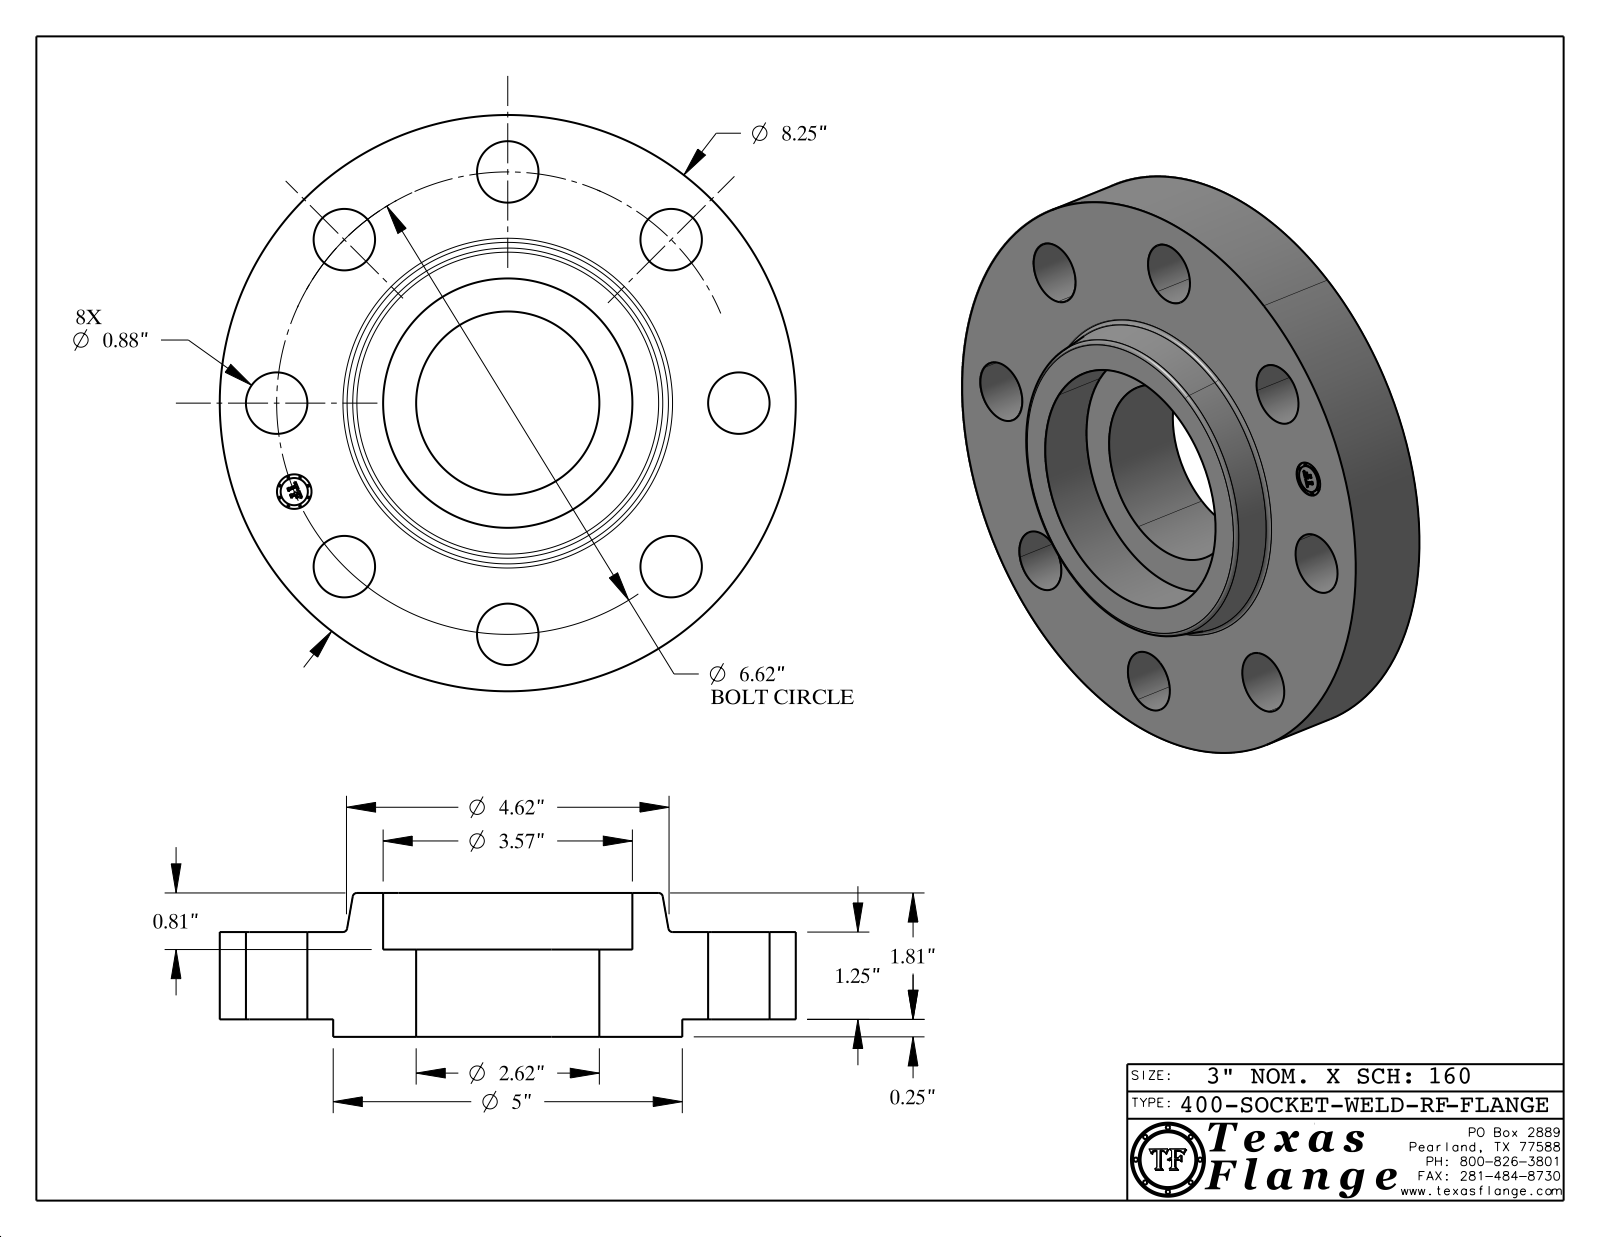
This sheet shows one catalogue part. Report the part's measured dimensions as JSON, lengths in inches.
{"part_name": "400-SOCKET-WELD-RF", "step_written_by": "CATIA V5 STEP AP214 (AUTOMOTIVE_DESIGN)", "units": "inches", "bodies": {"solids": 1, "faces": 420, "planar": 370, "cylindrical": 44, "other": 6}, "overall_size": [8.25, 8.25, 2.06], "volume_in3": 59.77, "surface_area_in2": 176, "round_holes": [[0.88, 8], [0.495, 1], [2.624, 1], [3.57, 1]], "round_bosses_or_shafts": [[0.03, 8], [8.25, 1], [5, 1], [0.39, 1]], "face_to_face_distances": [1.25, 0.25, 1.5, 2.06, 1.81, 0.56, 1, 0.81, 0.015, 1.485], "hole_center_spacings": [3.31, 2.533, 6.116, 4.681, 4.681, 1.291, 3.678, 6.493]}
